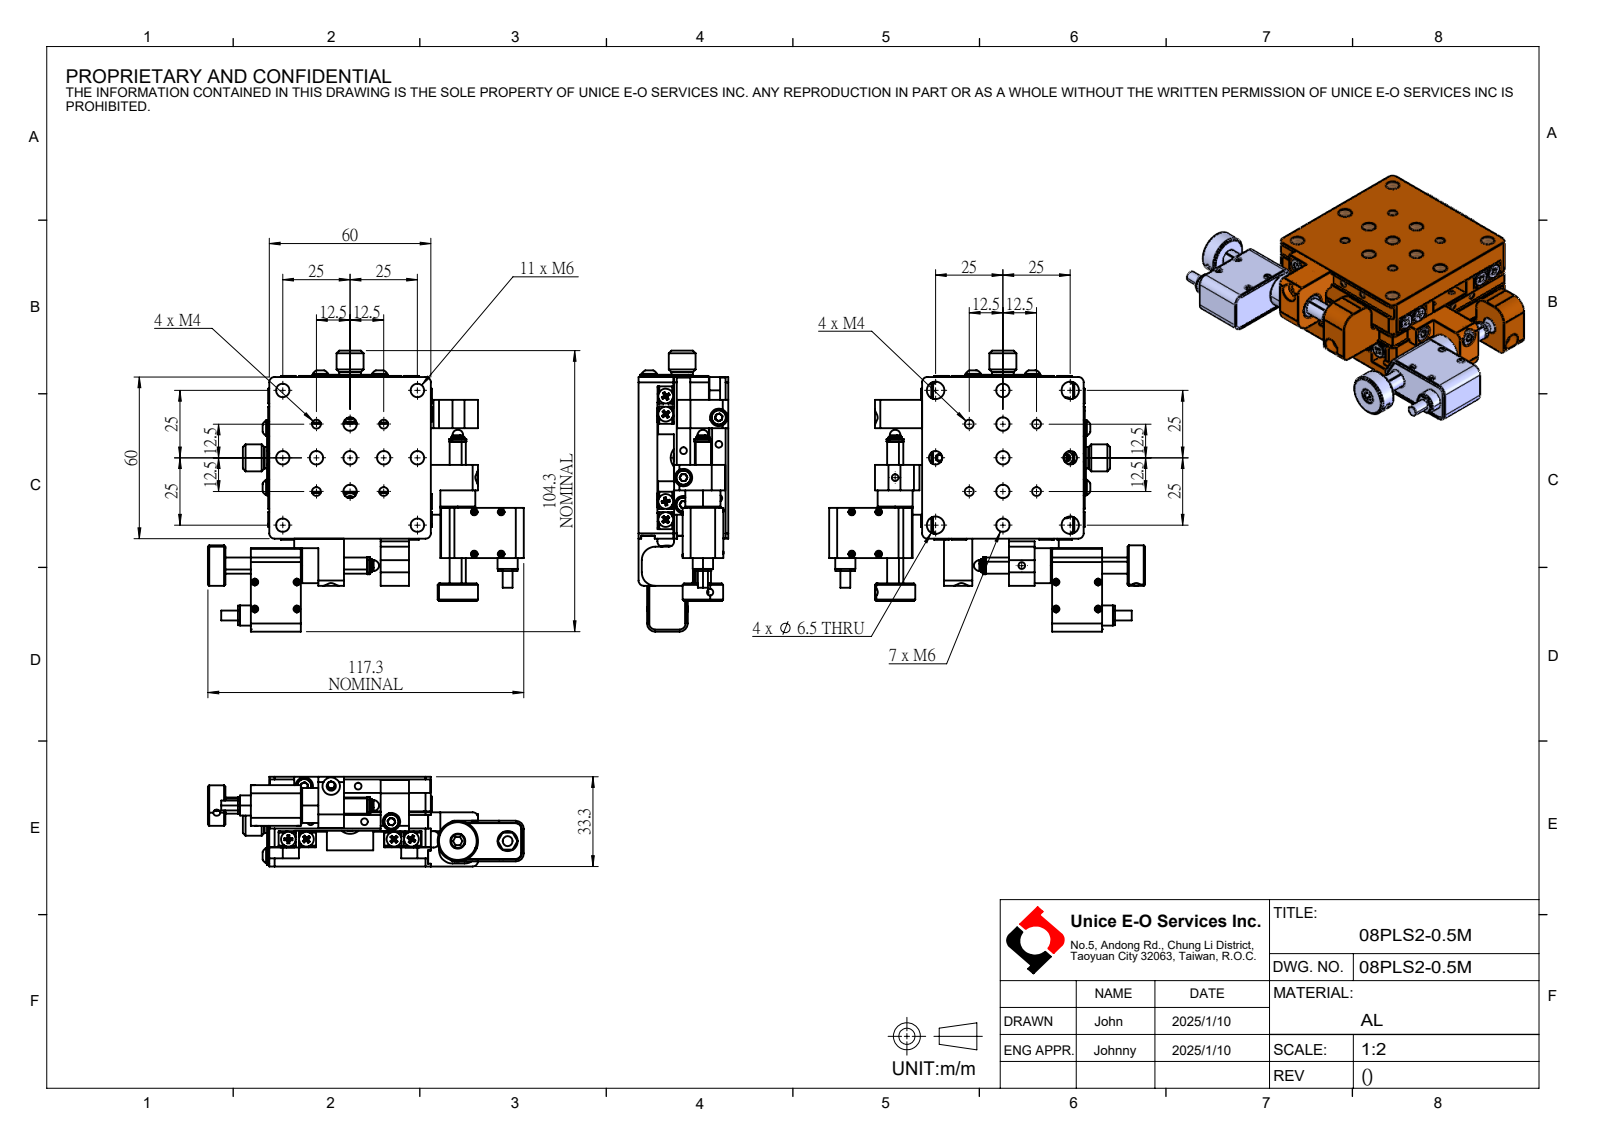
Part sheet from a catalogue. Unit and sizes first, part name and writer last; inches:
Units: inches
Overall size (bounding box): 4.617 × 4.106 × 1.311
Round holes (diameter × count): ⌀0.081 ×40, ⌀0.197 ×39, ⌀0.098 ×33, ⌀0.118 ×24, ⌀0.256 ×10, ⌀0.134 ×6, ⌀0.055 ×4, ⌀0.079 ×4, ⌀0.126 ×4, ⌀0.13 ×4, ⌀0.138 ×4, ⌀0.236 ×3
Round bosses / shafts (diameter × count): ⌀0.118 ×20, ⌀0.217 ×16, ⌀0.236 ×6, ⌀0.224 ×4, ⌀0.079 ×4, ⌀0.055 ×4, ⌀0.591 ×2, ⌀0.394 ×2
Partial cylindrical surfaces — rounded edges, fillets, slot ends (radius × count): R0.079 ×18, R0.197 ×8, R0.069 ×4, R0.118 ×4, R0.236 ×4
Main face-to-face distances: 0.516, 0.52, 0.276, 0.24, 0.28, 0.795, 0.236, 0.791, 0.512, 1.031
Hole centre spacings: 0.787, 0.984, 0.696, 1.556, 0.394, 1.1, 1.392, 0.492
Bodies: 0 solids, 3642 faces (1284 planar, 995 cylindrical, 1363 other)
Part name (STEP PRODUCT): 08PLS2-0.5M
STEP written by: SolidWorks 2024 (CONFIG_CONTROL_DESIGN)
